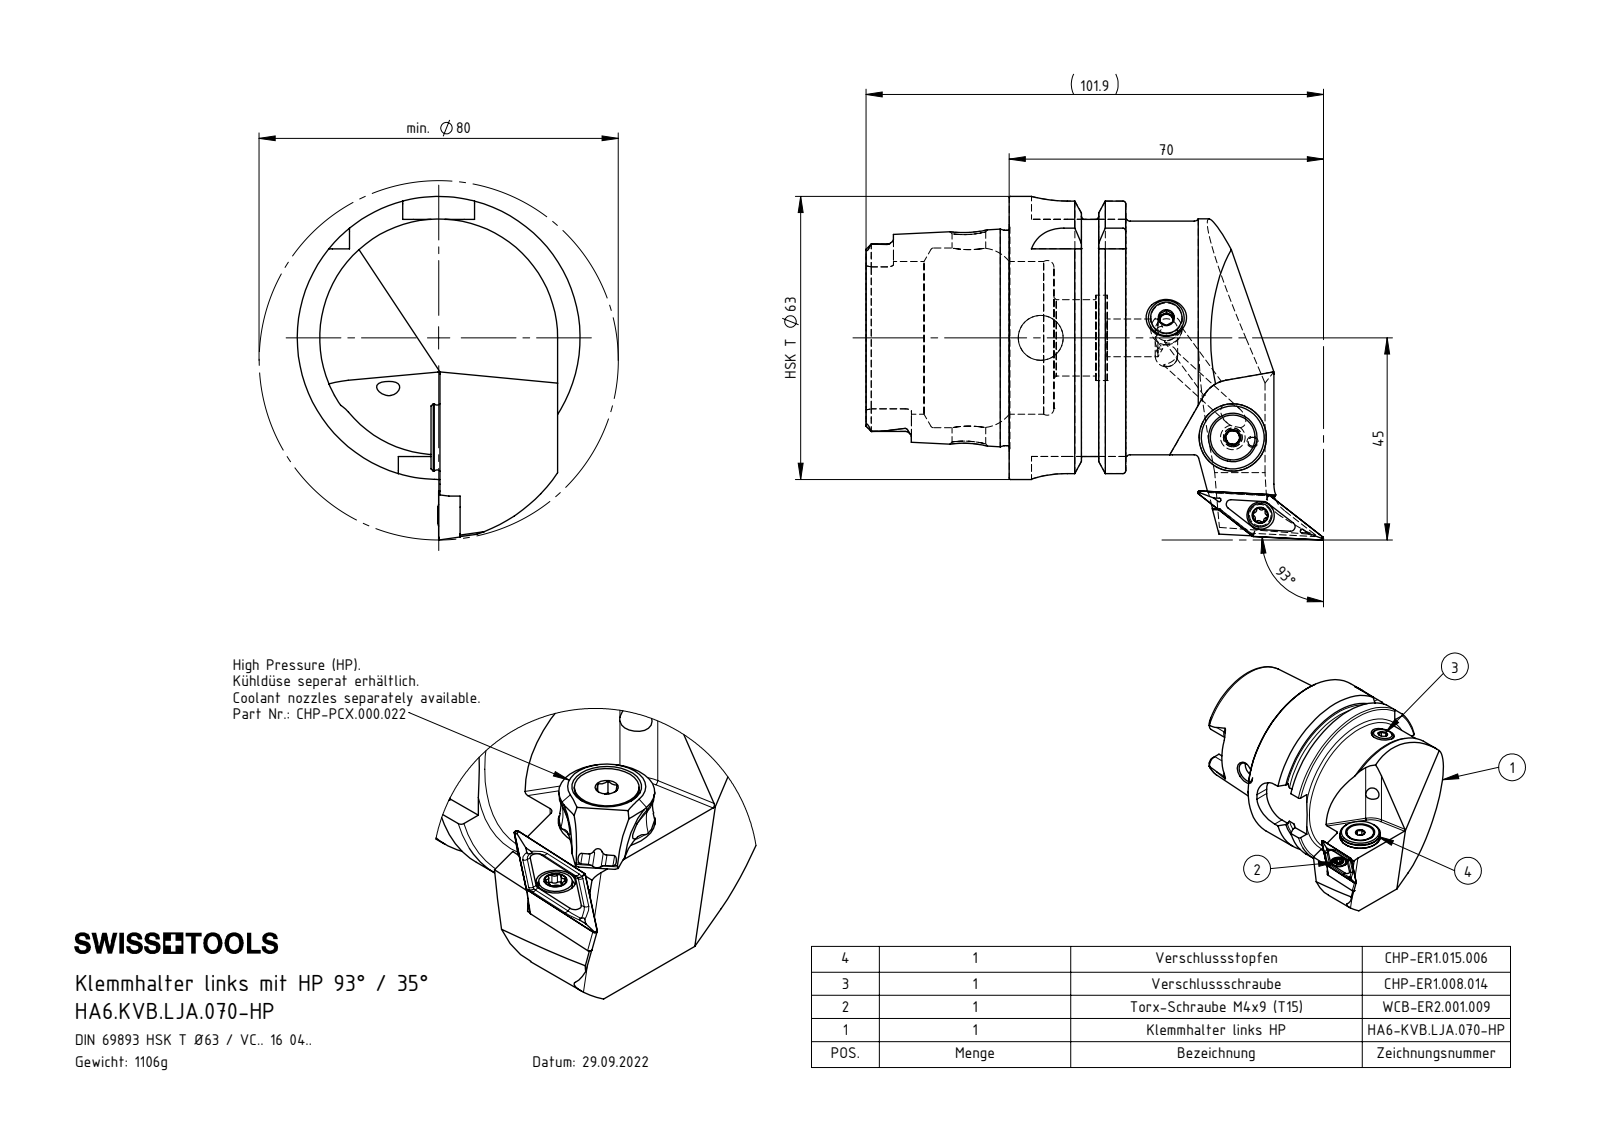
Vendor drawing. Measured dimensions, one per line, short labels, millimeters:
name: HA6.KVB.LJA.070-HP; CHP-ER1.008.014_A; ISO 8752 2x8; VCMT160404 (+6 more)
written by: SolidWorks 2017 (AUTOMOTIVE_DESIGN)
unit: mm
bodies: 8 solids, 419 faces (122 planar, 117 cylindrical, 180 other)
size: 101.9 × 76.5 × 63
volume: 140 299 mm³; area: 32 676 mm²
holes: 2× ⌀4.2, 2× ⌀5, 1× ⌀1.2, 1× ⌀2, 1× ⌀2.5, 1× ⌀3, 1× ⌀3.3, 1× ⌀4.4, 1× ⌀5.2, 1× ⌀6.1, 1× ⌀7, 1× ⌀7.5
bosses: 1× ⌀63, 1× ⌀54.95, 1× ⌀52, 1× ⌀47.94, 1× ⌀15, 1× ⌀13.4, 1× ⌀10, 1× ⌀8
rounds: 6× R0.34, 6× R0.59, 6× R1.4, 4× R8, 2× R0.5, 2× R2.82, 2× R2.88, 2× R7
face distances: 25.95, 16, 9.95, 31.9, 41.85, 57.85, 52.8, 21.8, 26.2, 11.85
hole spacings: 4.5, 16.44, 16.49, 18.37, 18.44, 48.19, 52.54, 62.85
